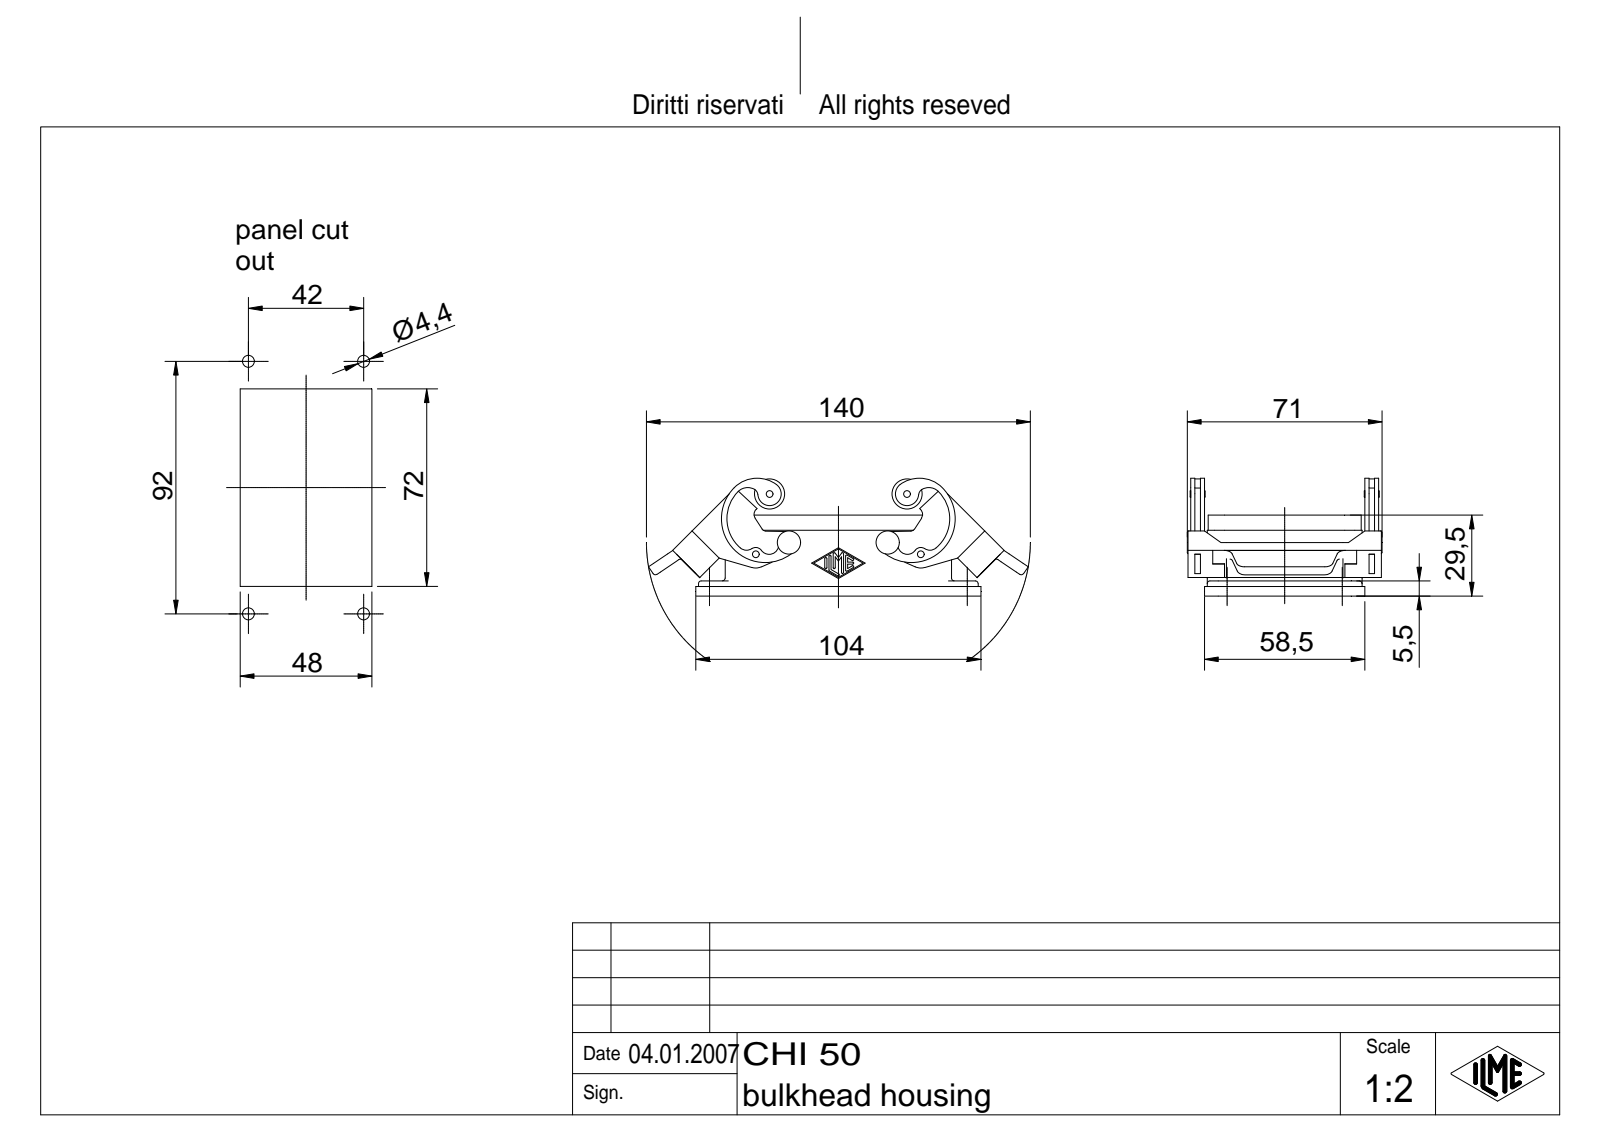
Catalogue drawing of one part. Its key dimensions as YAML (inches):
part_name: "CHI_50"
step_written_by: "Creo Elements/Direct Modeling 18.1F 24-Jul-2014 (C) Parametric Technology GmbH (AUTOMOTIVE_DESIGN)"
units: inches
bodies: {solids: 1, faces: 636, planar: 266, cylindrical: 310, other: 60}
overall_size: [5.036, 2.795, 1.691]
volume: 3.364
surface_area: 58.91
round_holes:
  - {diameter: 0.097, count: 8}
  - {diameter: 0.122, count: 8}
  - {diameter: 0.173, count: 4}
round_bosses_or_shafts:
  - {diameter: 0.098, count: 4}
  - {diameter: 0.433, count: 2}
  - {diameter: 0.197, count: 2}
partial_cylinders:
  - {radius: 0.039, count: 46}
  - {radius: 0.015, count: 14}
  - {radius: 0.059, count: 10}
  - {radius: 0.098, count: 10}
  - {radius: 0.157, count: 10}
  - {radius: 0.197, count: 8}
  - {radius: 0.236, count: 8}
  - {radius: 0.114, count: 4}
face_to_face_distances: [0.118, 0.217, 0.138, 2.5, 2.106, 0.059, 0.039, 0.177, 0.157, 0.079]
hole_center_spacings: [0.513, 0.63, 0.843, 0.945, 1.109, 1.693, 2.598, 2.674]
